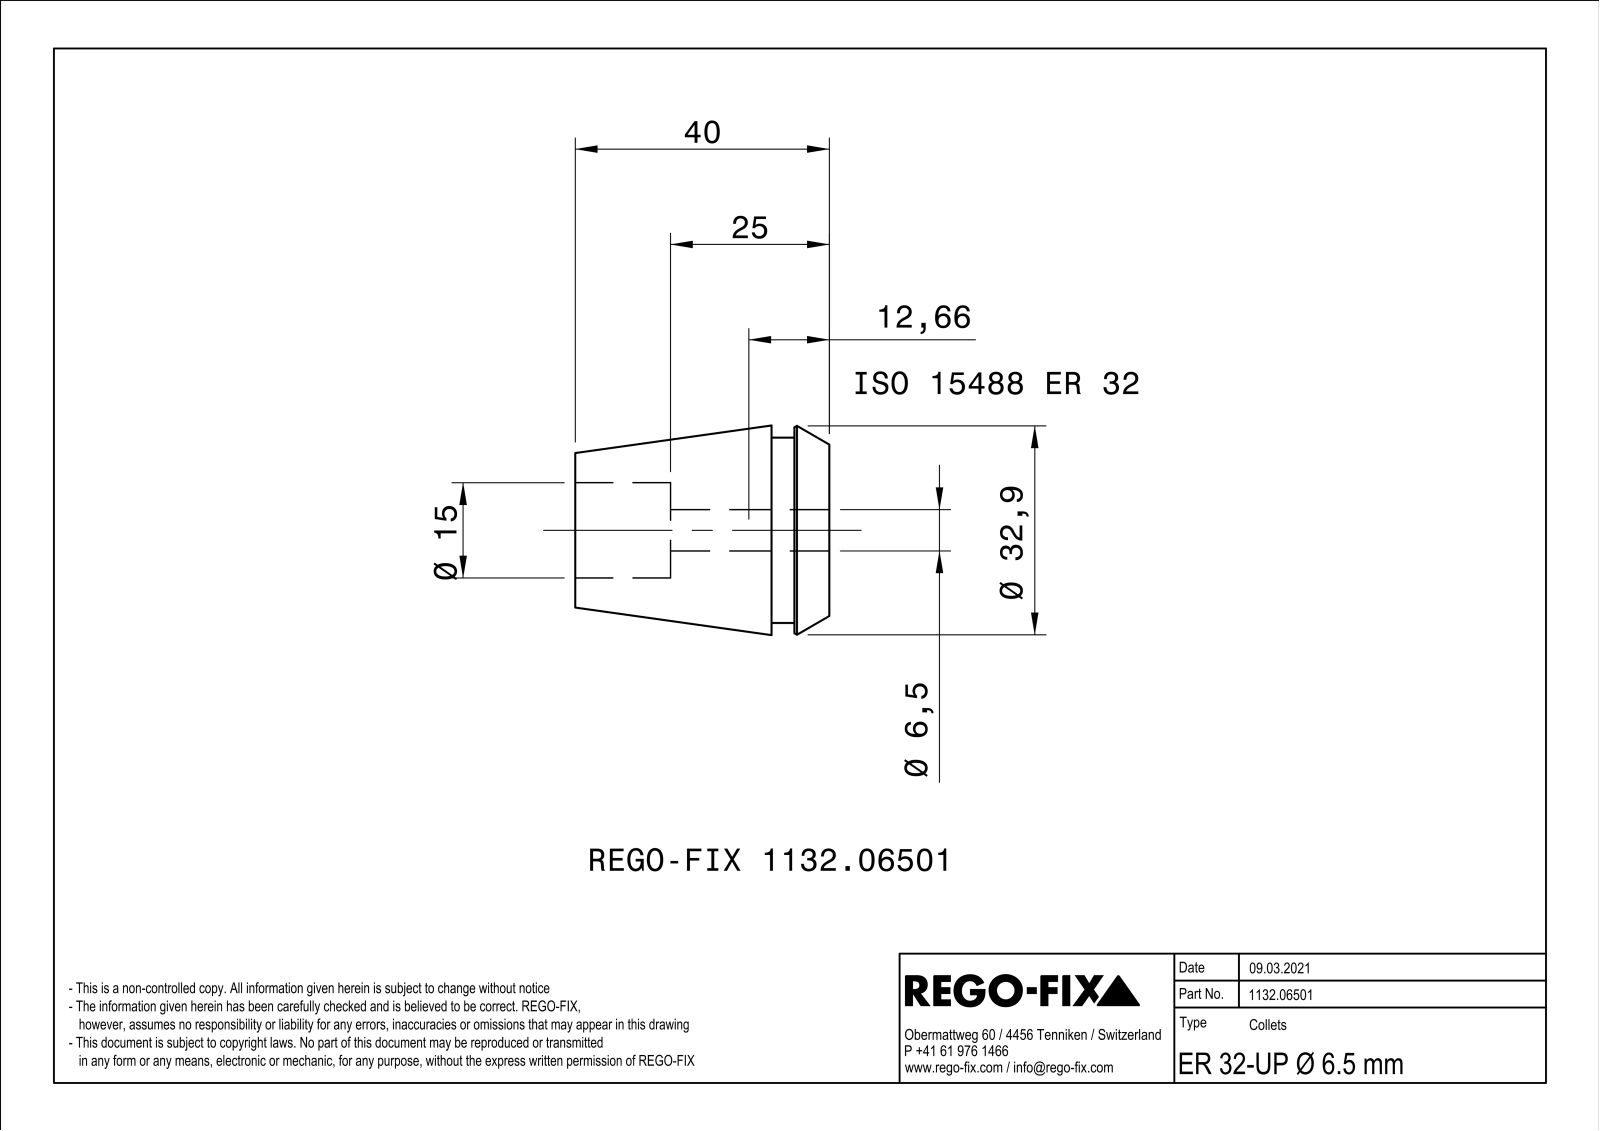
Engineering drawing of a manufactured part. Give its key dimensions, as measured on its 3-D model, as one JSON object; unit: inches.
{"part_name": "NOCUT", "step_written_by": "SIEMENS PLM Software Solid Edge ST10 (AUTOMOTIVE_DESIGN)", "units": "inches", "bodies": {"solids": 1, "faces": 256, "planar": 88, "cylindrical": 48, "other": 120}, "overall_size": [1.575, 1.299, 1.299], "volume_in3": 1.177, "surface_area_in2": 22.54, "round_holes": [[0.591, 1]], "round_bosses_or_shafts": [[1.15, 1]], "partial_cylinders_radius": [[0.016, 13], [0.128, 1]], "face_to_face_distances": [0.031, 0.032, 0.031, 1.575, 0.358, 1.217, 0.217, 0.142, 1.358, 0.984]}
